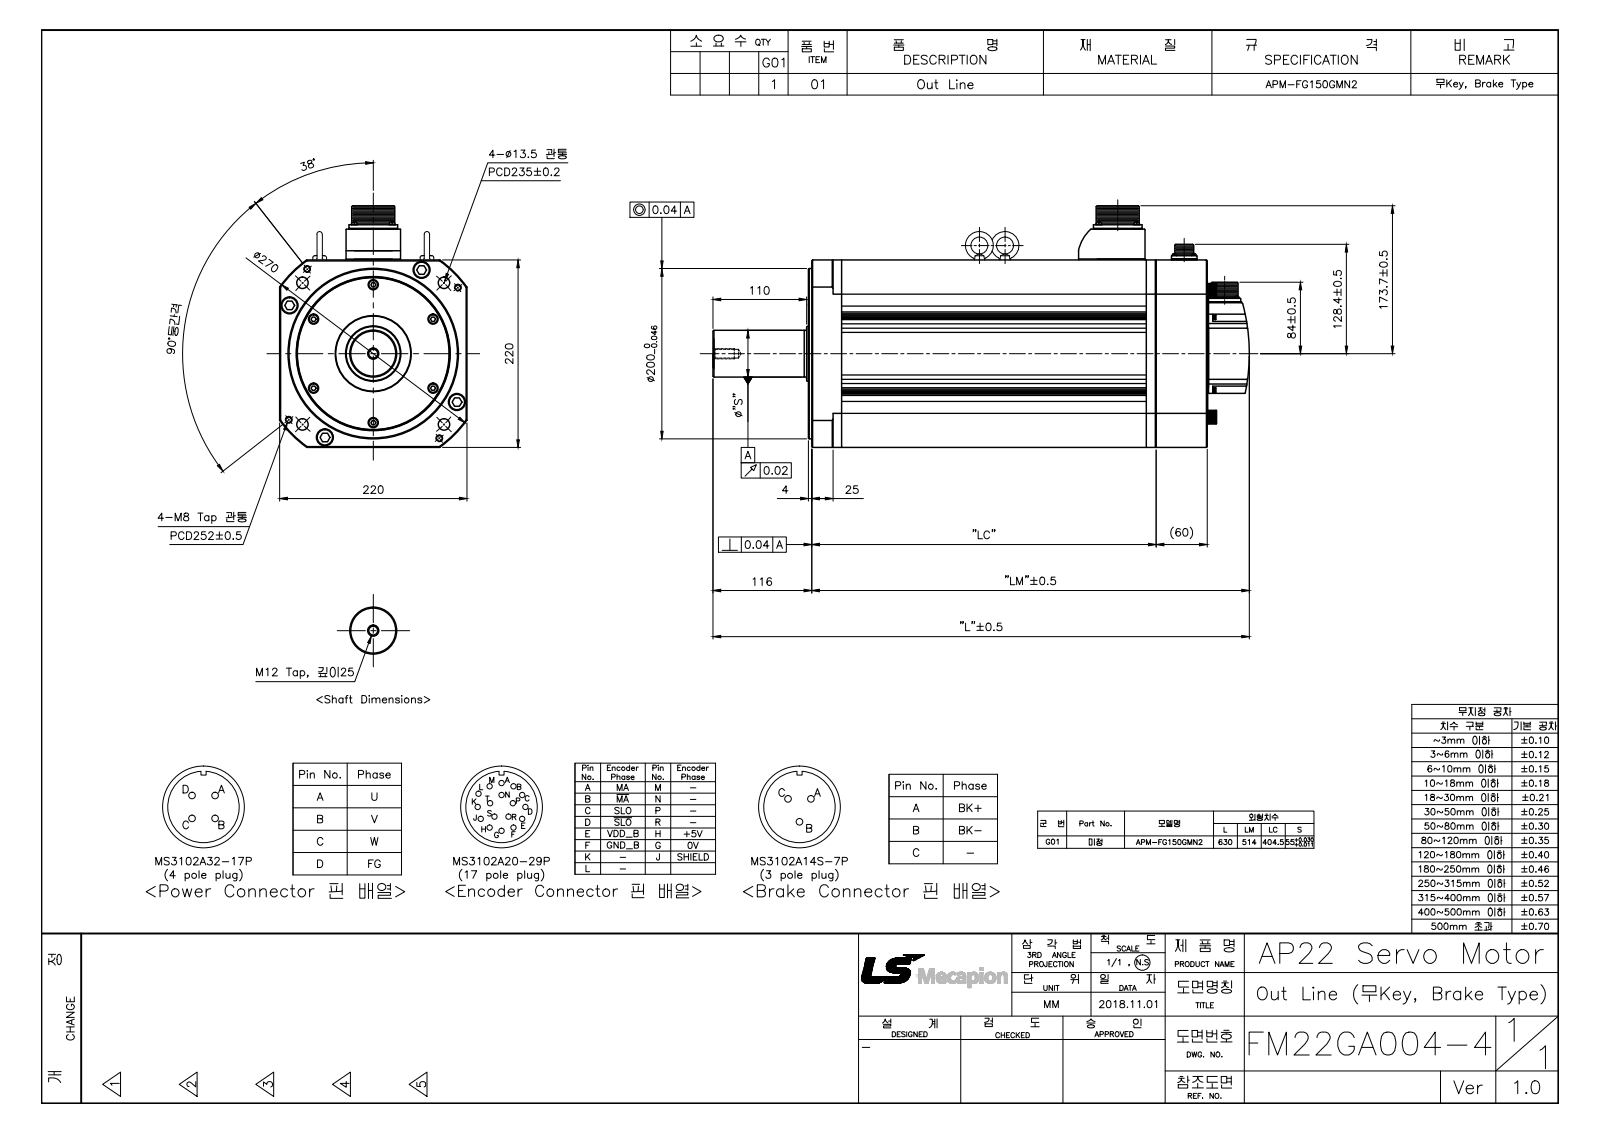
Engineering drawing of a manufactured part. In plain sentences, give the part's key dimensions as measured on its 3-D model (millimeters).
The part is named "FM22GA004-4_Out Line(APM-FG150G_N2)". Its 3-D file was written by "SolidWorks 2011 (AUTOMOTIVE_DESIGN)". It is 81 solids with 2544 faces: 915 planar, 1004 cylindrical and 625 other. Overall it measures 630 by 283.7 by 220 millimeters. Its volume is 20 230 000 cubic millimeters and its surface area 1 167 000 square millimeters. Round holes: 12 of diameter 2.5, 12 of diameter 3, 10 of diameter 3.05, 10 of diameter 6.8, 10 of diameter 12, 8 of diameter 8, 8 of diameter 13.5, 8 of diameter 20, 6 of diameter 5, 6 of diameter 6, 6 of diameter 7, 5 of diameter 10.2. Round bosses or shafts: 20 of diameter 1.6, 9 of diameter 10, 8 of diameter 5.4, 6 of diameter 10.2, 4 of diameter 18, 4 of diameter 7, 4 of diameter 6, 4 of diameter 5.5. Partial cylindrical surfaces (rounded edges, fillets, slot ends): 112 of radius 1, 17 of radius 2, 16 of radius 5, 12 of radius 4.5, 8 of radius 0.5, 4 of radius 2.5, 4 of radius 4, 4 of radius 6. The main face-to-face distances are 11.5, 40, 369.5, 358, 220, 180, 140, 14, 5, 21. The hole center spacings are 81, 43.49, 118.14, 140.3, 161.32, 16.26, 17.11, 20.79.
